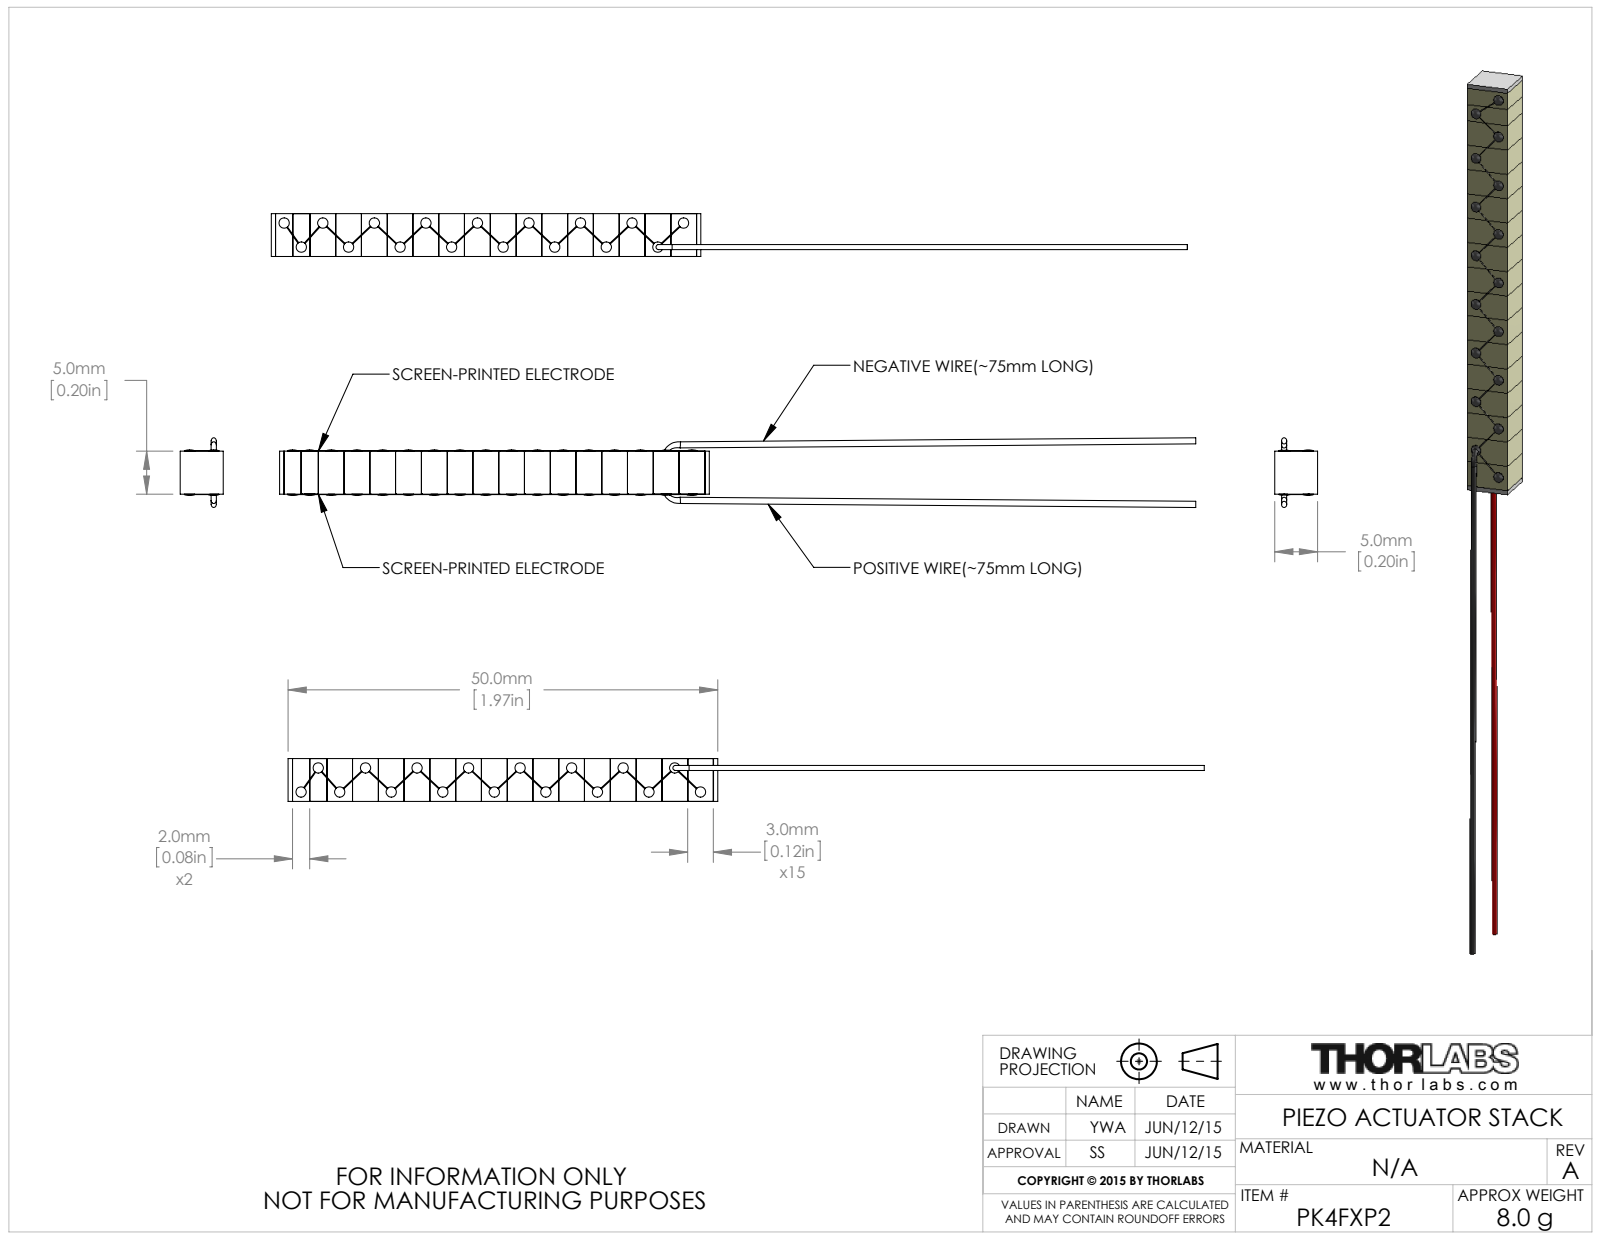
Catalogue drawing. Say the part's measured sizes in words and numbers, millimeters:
The part is named "CTN003050". Its 3-D file was written by "SolidWorks 2014 (AUTOMOTIVE_DESIGN)". It is 48 solids with 386 faces: 178 planar, 132 cylindrical and 76 other. Overall it measures 106.66 by 8.12 by 5 millimeters. Its volume is 1 497 cubic millimeters and its surface area 2 636 square millimeters. Round bosses or shafts: 17 of diameter 1.2. The main face-to-face distances are 3, 6, 9, 5, 12, 15, 18, 21, 24, 27.
